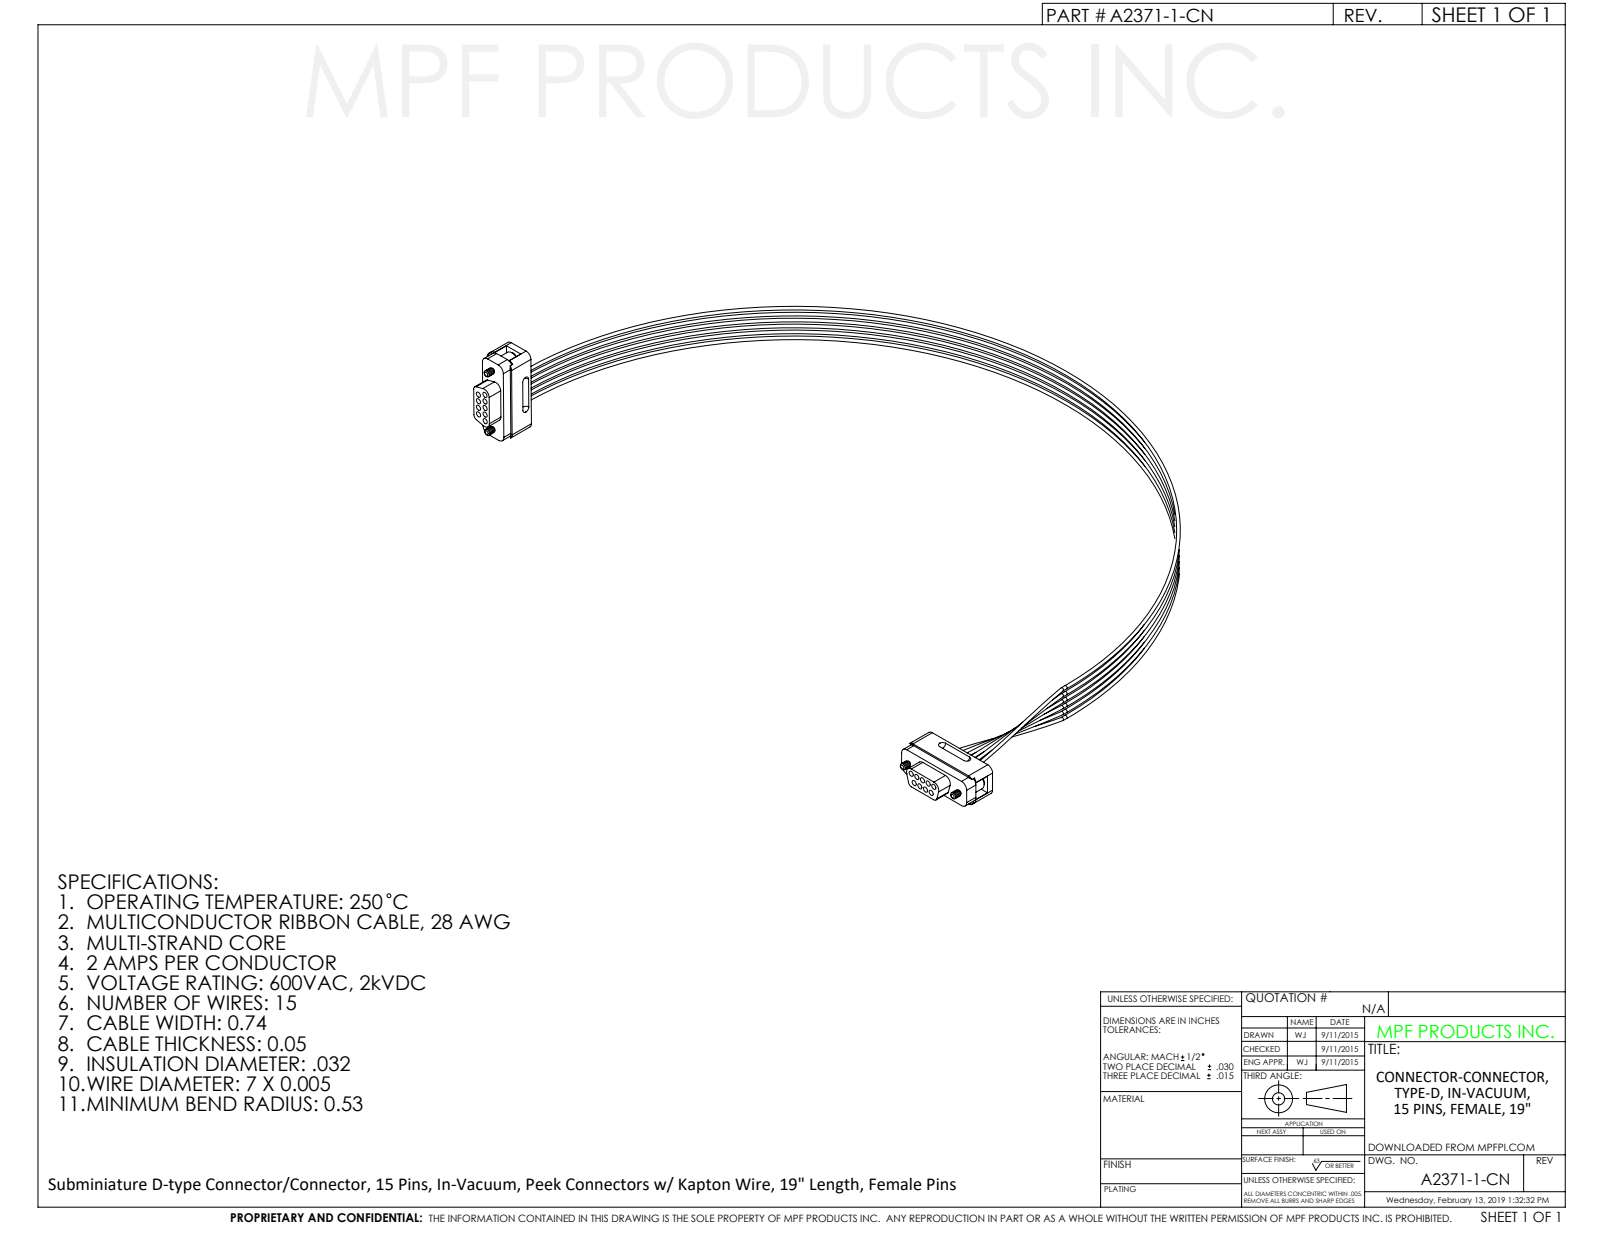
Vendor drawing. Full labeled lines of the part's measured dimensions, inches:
Part name (STEP PRODUCT): A2371-1-CN
STEP written by: SolidWorks 2012 (CONFIG_CONTROL_DESIGN)
Units: inches
Bodies: 0 solids, 402 faces (105 planar, 165 cylindrical, 132 other)
Overall size (bounding box): 11.34 × 8.855 × 1.601
Round holes (diameter × count): ⌀0.08 ×40, ⌀0.11 ×4, ⌀0.15 ×4, ⌀0.051 ×1, ⌀0.054 ×1
Round bosses / shafts (diameter × count): ⌀0.139 ×3, ⌀0.237 ×2, ⌀0.056 ×2, ⌀0.056 ×2
Partial cylindrical surfaces — rounded edges, fillets, slot ends (radius × count): R0.1 ×12, R0.068 ×4, R0.07 ×4, R0.093 ×4, R0.05 ×2, R0.055 ×2, R0.08 ×2, R0.118 ×2
Main face-to-face distances: 0.475, 0.032, 0.439, 0.407, 0.443, 0.036, 0.476, 0.52, 0.05, 0.496
Hole centre spacings: 0.22, 0.33, 0.11, 0.55, 0.11, 0.44, 0.13, 0.126
